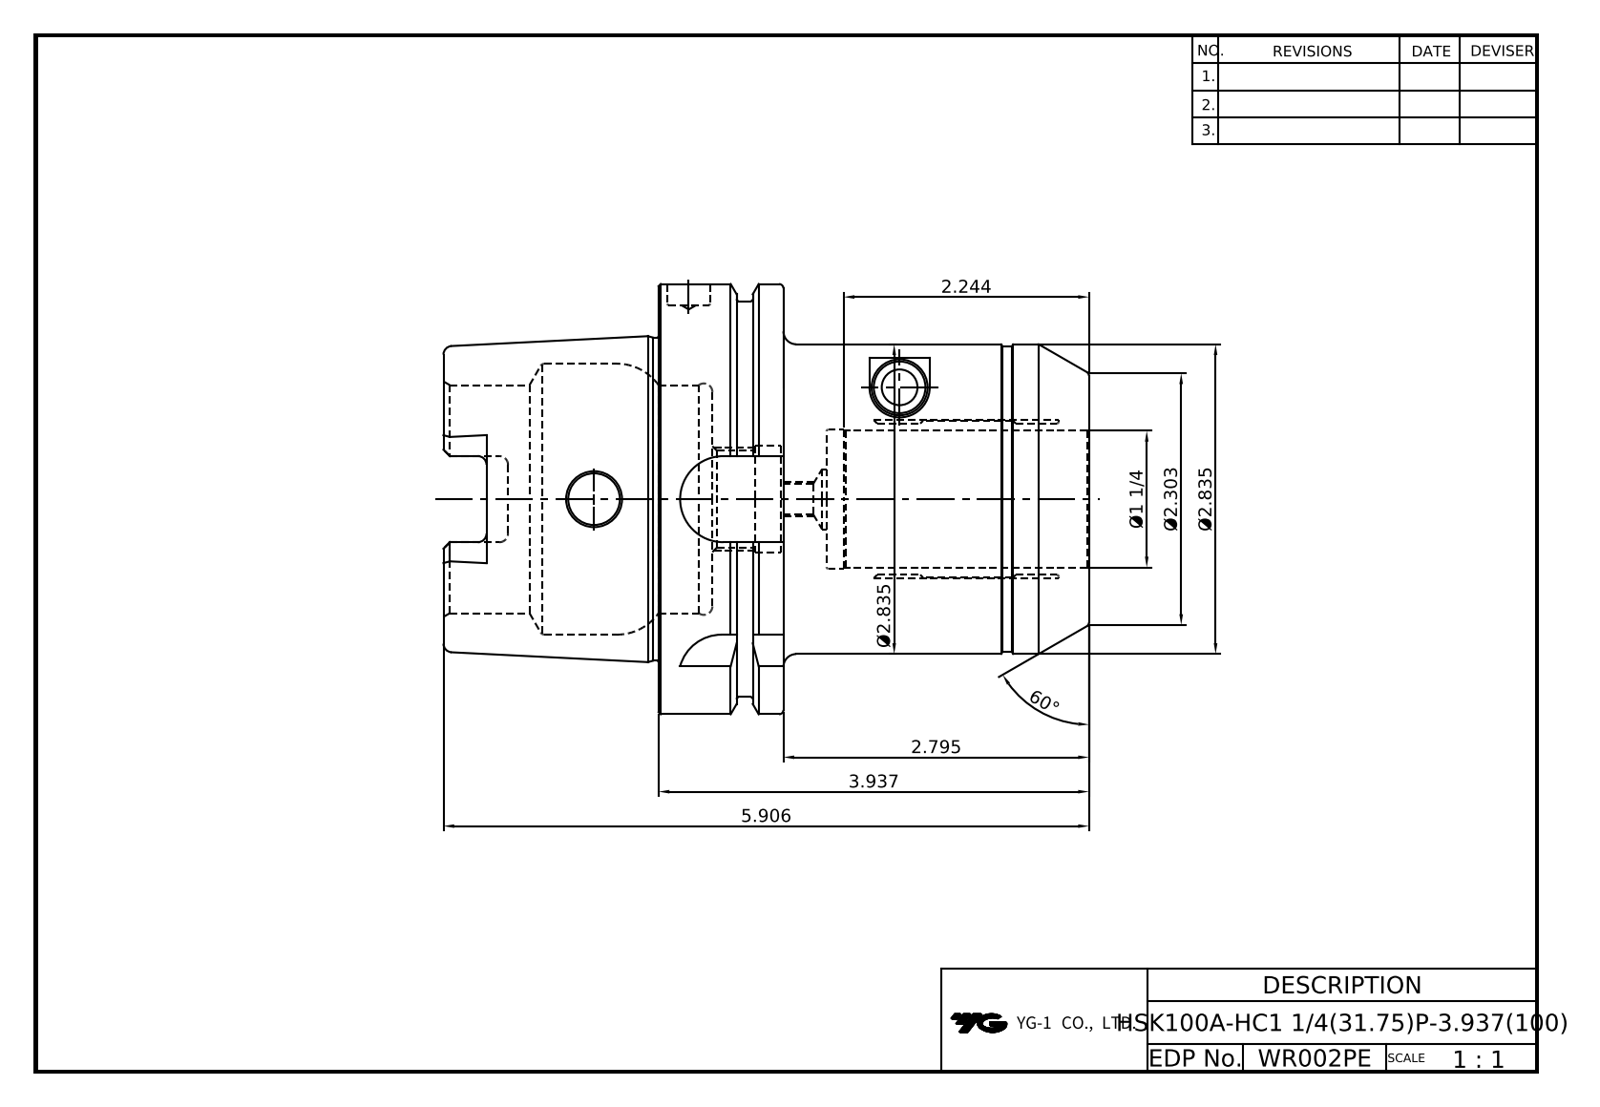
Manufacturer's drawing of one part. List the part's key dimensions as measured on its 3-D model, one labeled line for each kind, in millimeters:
Part name (STEP PRODUCT): LO-HSK100A-HC31.75P-100
STEP written by: Autodesk Inventor 2020 (AUTOMOTIVE_DESIGN)
Units: millimetres
Bodies: 1 solid, 124 faces (38 planar, 37 cylindrical, 49 other)
Overall size (bounding box): 150 × 100 × 100
Volume: 485 985 mm³ · Surface area: 70 594 mm²
Round holes (diameter × count): ⌀6.92 ×1, ⌀10 ×1, ⌀12 ×1, ⌀14 ×1, ⌀22.38 ×1, ⌀25 ×1, ⌀31.75 ×1, ⌀32.55 ×1, ⌀53 ×1, ⌀63 ×1
Round bosses / shafts (diameter × count): ⌀100 ×1, ⌀92 ×1, ⌀75.41 ×1, ⌀72 ×1, ⌀71 ×1
Partial cylindrical surfaces — rounded edges, fillets, slot ends (radius × count): R2 ×6, R4.88 ×4, R10 ×4
Main face-to-face distances: 29, 100, 71, 12.5, 16.5, 87.5, 79, 62.5, 10, 50
